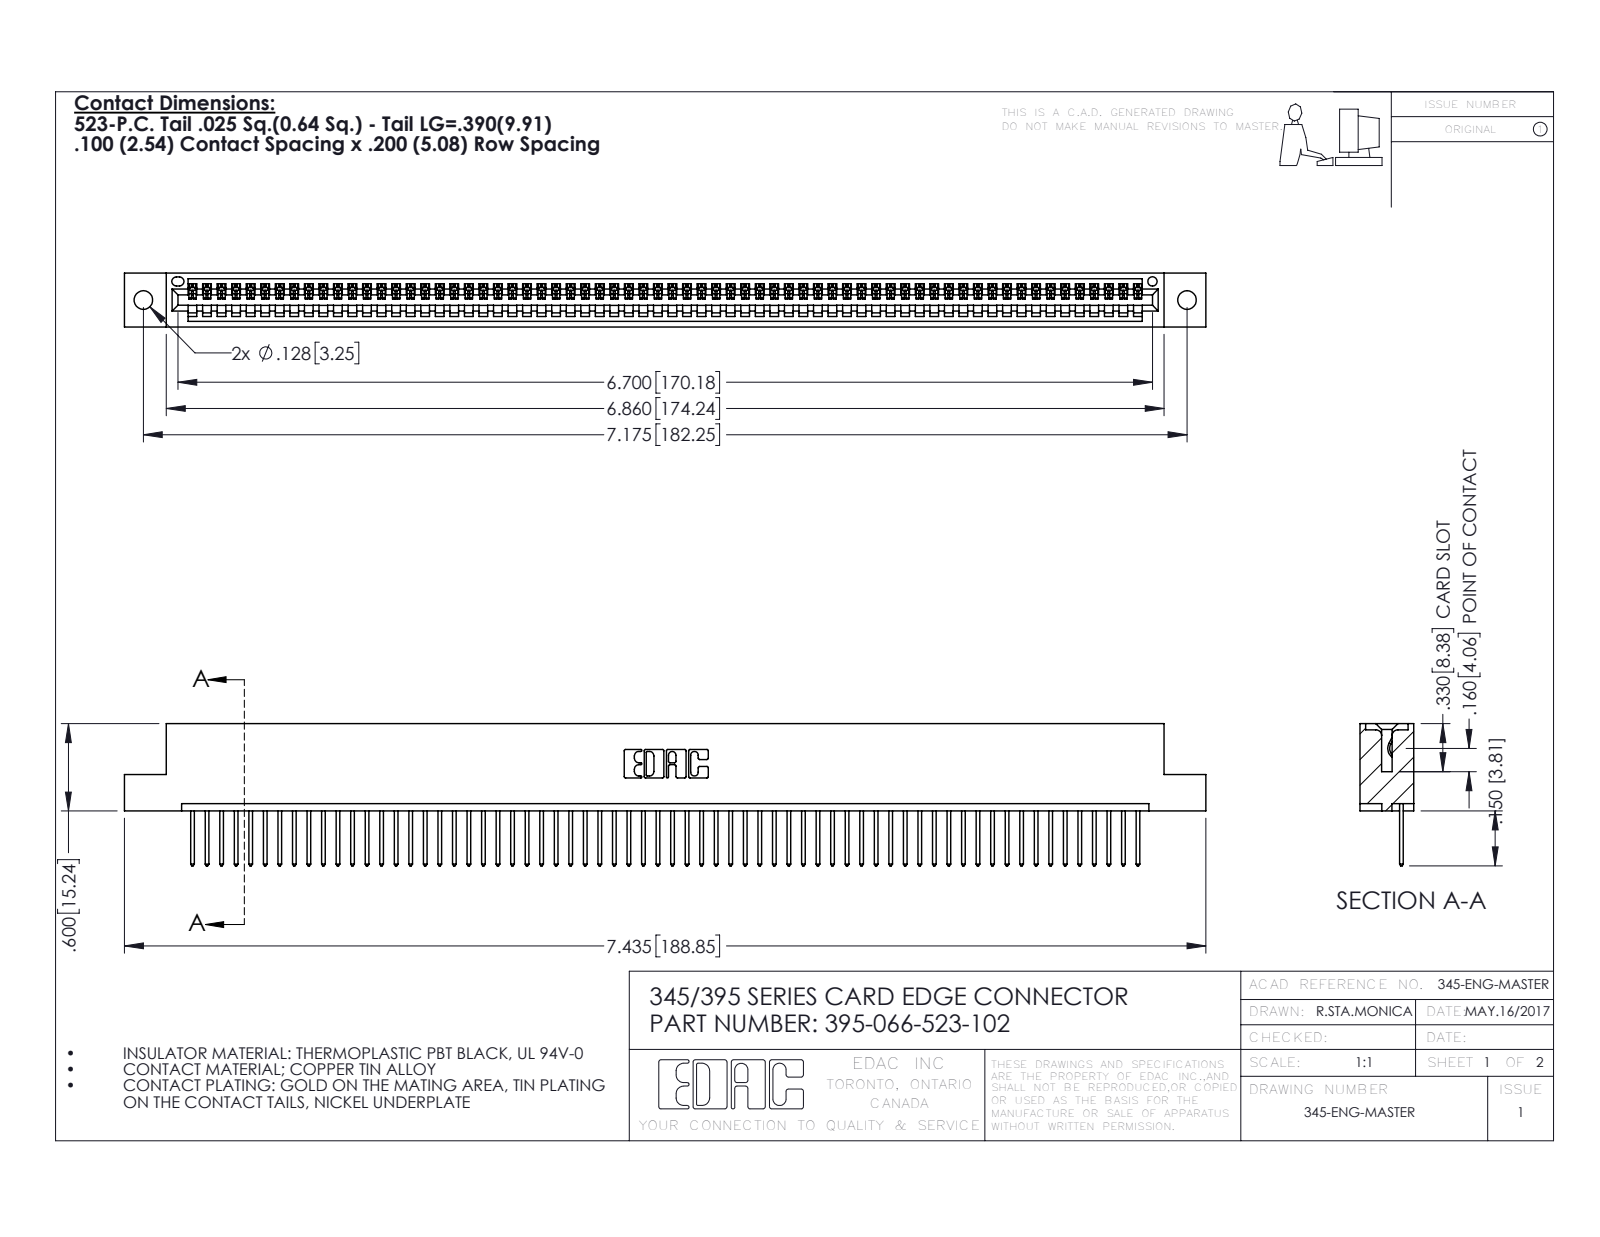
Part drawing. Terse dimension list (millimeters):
name: 395-066-523-102; 345 Part_Flush Mounting Lugs - 0.128 Dia; 345-292-001_345-293-123
written by: SolidWorks 2016 (CONFIG_CONTROL_DESIGN)
unit: mm
bodies: 67 solids, 3954 faces (2720 planar, 1234 cylindrical, 0 other)
size: 188.8 × 24.8 × 9.4
volume: 18 070 mm³; area: 24 140 mm²
holes: 2× ⌀3.3, 1× ⌀1.6
rounds: 132× R0.2, 132× R0.3, 22× R0.3, 6× R0.2, 6× R0.8, 3× R0.7, 2× R0.8, 2× R1
face distances: 7.6, 1.8, 9.4, 5.1, 2.5, 6.9, 0.6, 5.7, 3.8, 1.8
hole spacings: 6.9, 176.3, 182.2
